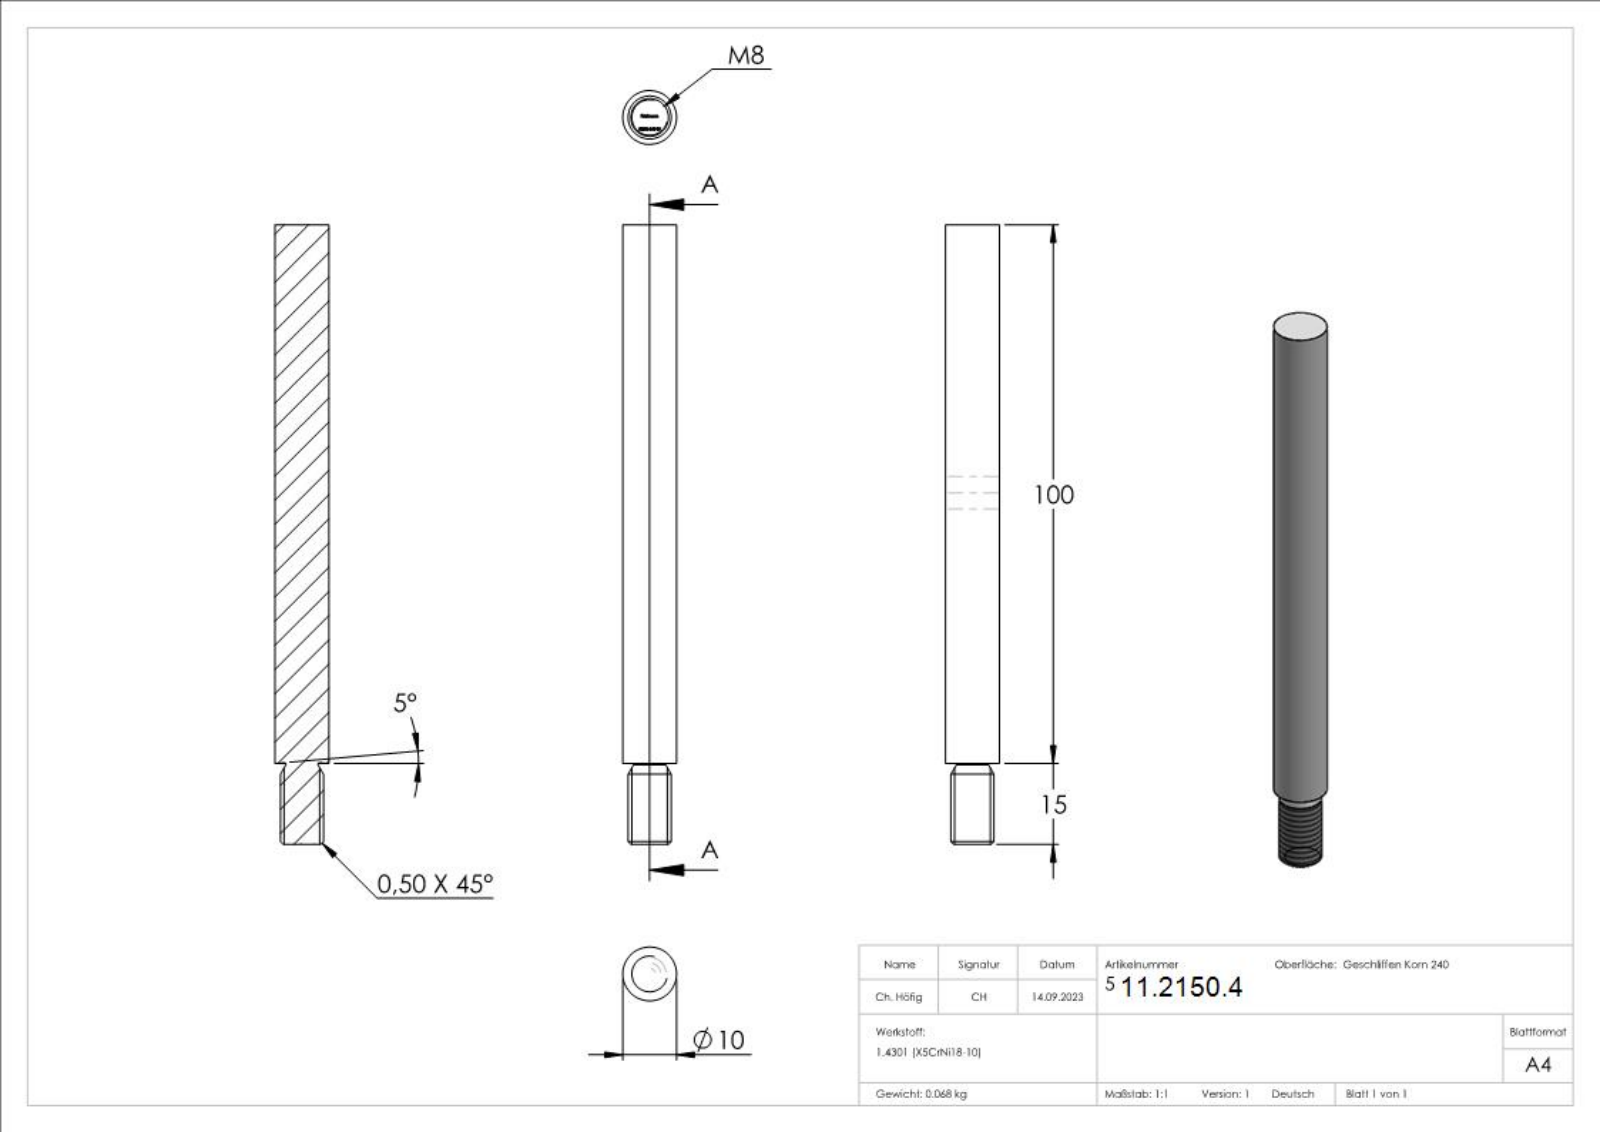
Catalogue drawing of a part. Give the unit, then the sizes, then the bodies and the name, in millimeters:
Units: millimetres
Overall size (bounding box): 115 × 10 × 10
Round bosses / shafts (diameter × count): ⌀10 ×1, ⌀8 ×1
Main face-to-face distances: 115, 114.9, 0.77, 1.29, 2.38, 2.39, 0.72, 1.55, 2.44, 0.57
Volume: 8 575 mm³ · Surface area: 3 695 mm²
Bodies: 1 solid, 266 faces (157 planar, 2 cylindrical, 107 other)
Part name (STEP PRODUCT): 50236-240-10
STEP written by: SolidWorks 2018 (CONFIG_CONTROL_DESIGN)
